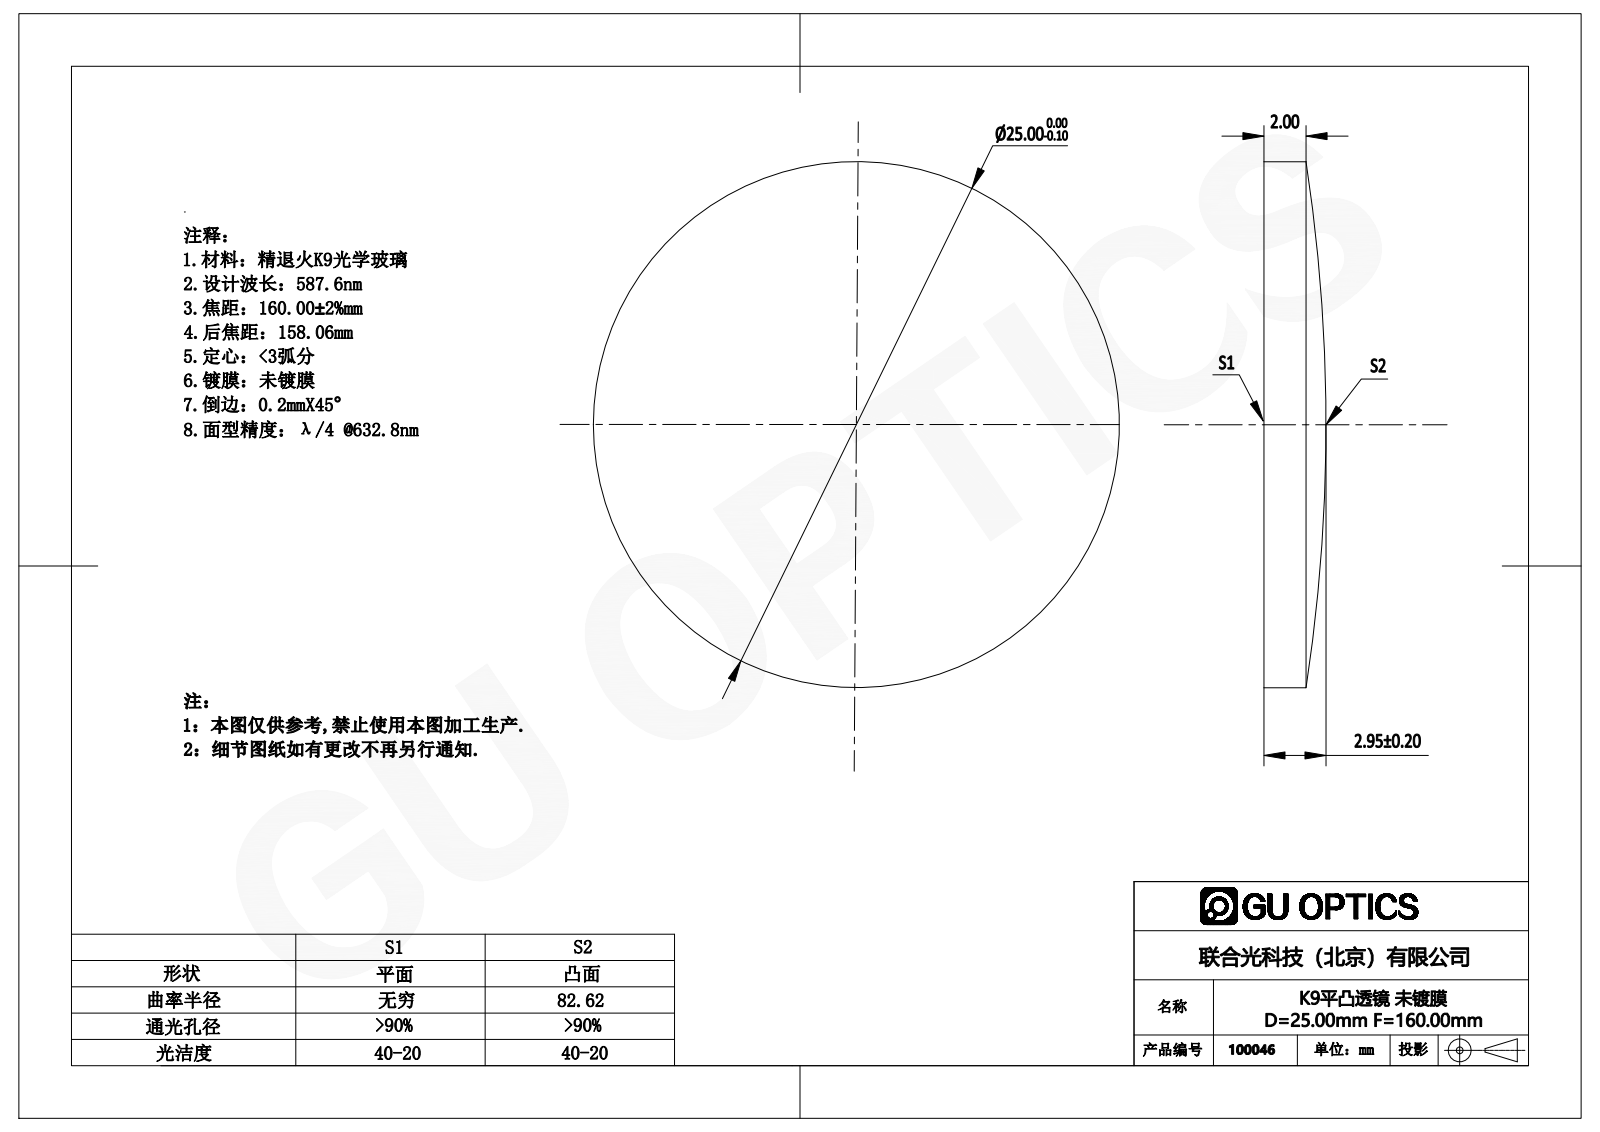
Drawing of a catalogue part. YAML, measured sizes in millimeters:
part_name: "100046"
step_written_by: "SolidWorks 2016 (AUTOMOTIVE_DESIGN)"
units: millimeters
bodies: {solids: 1, faces: 5, planar: 1, cylindrical: 2, other: 2}
overall_size: [25, 25, 2.95]
volume: 1215
surface_area: 1142
round_bosses_or_shafts:
  - {diameter: 25, count: 1}
